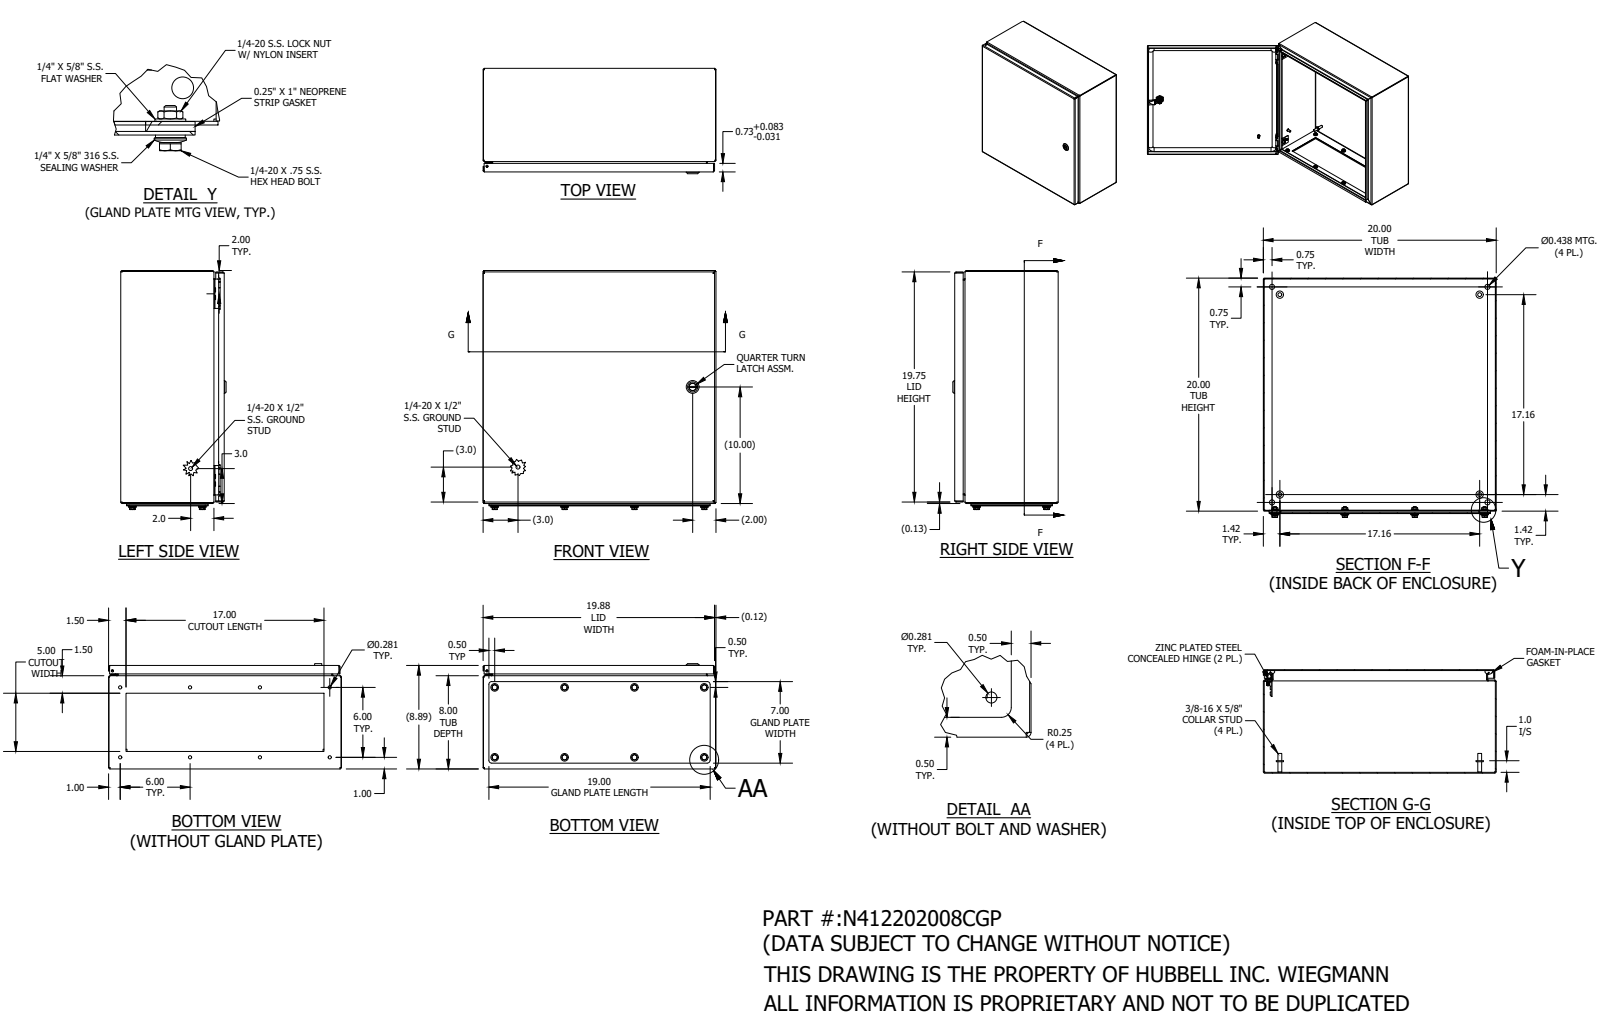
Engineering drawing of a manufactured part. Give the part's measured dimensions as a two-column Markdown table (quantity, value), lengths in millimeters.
| quantity | value |
| --- | --- |
| part name | N412202008CGP |
| STEP written by | SolidWorks 2019 (AUTOMOTIVE_DESIGN) |
| units | millimeters |
| bodies | 71 solids, 2035 faces (794 planar, 624 cylindrical, 617 other) |
| overall size | 521.2 × 508 × 229.7 |
| volume | 2 383 000 mm³ |
| surface area | 2 318 000 mm² |
| round holes (diameter × count) | 4.1 × 8, 5.4 × 8, 7.1 × 8, 7.4 × 8, 8.9 × 6, 4.8 × 5, 2.4 × 4, 4.2 × 4, 6 × 4, 6 × 4, 7 × 4, 7 × 4 |
| round bosses / shafts (diameter × count) | 6.4 × 18, 16.5 × 8, 15.2 × 8, 11.1 × 8, 15.9 × 7, 15.9 × 5, 9.1 × 4, 8.4 × 4 |
| partial cylindrical surfaces (radius × count) | 0.3 × 30, 1.3 × 26, 1.2 × 20, 3.1 × 20, 0.5 × 13, 3.2 × 8, 3.3 × 8, 4 × 5 |
| main face-to-face distances | 1.9, 223.8, 221.9, 225.7, 511.3, 506.1, 504.2, 1.9, 506.1, 508 |
| hole center spacings | 152.4, 215.5, 304.8, 406.5, 340.8, 469.9, 16.7, 16.8 |
